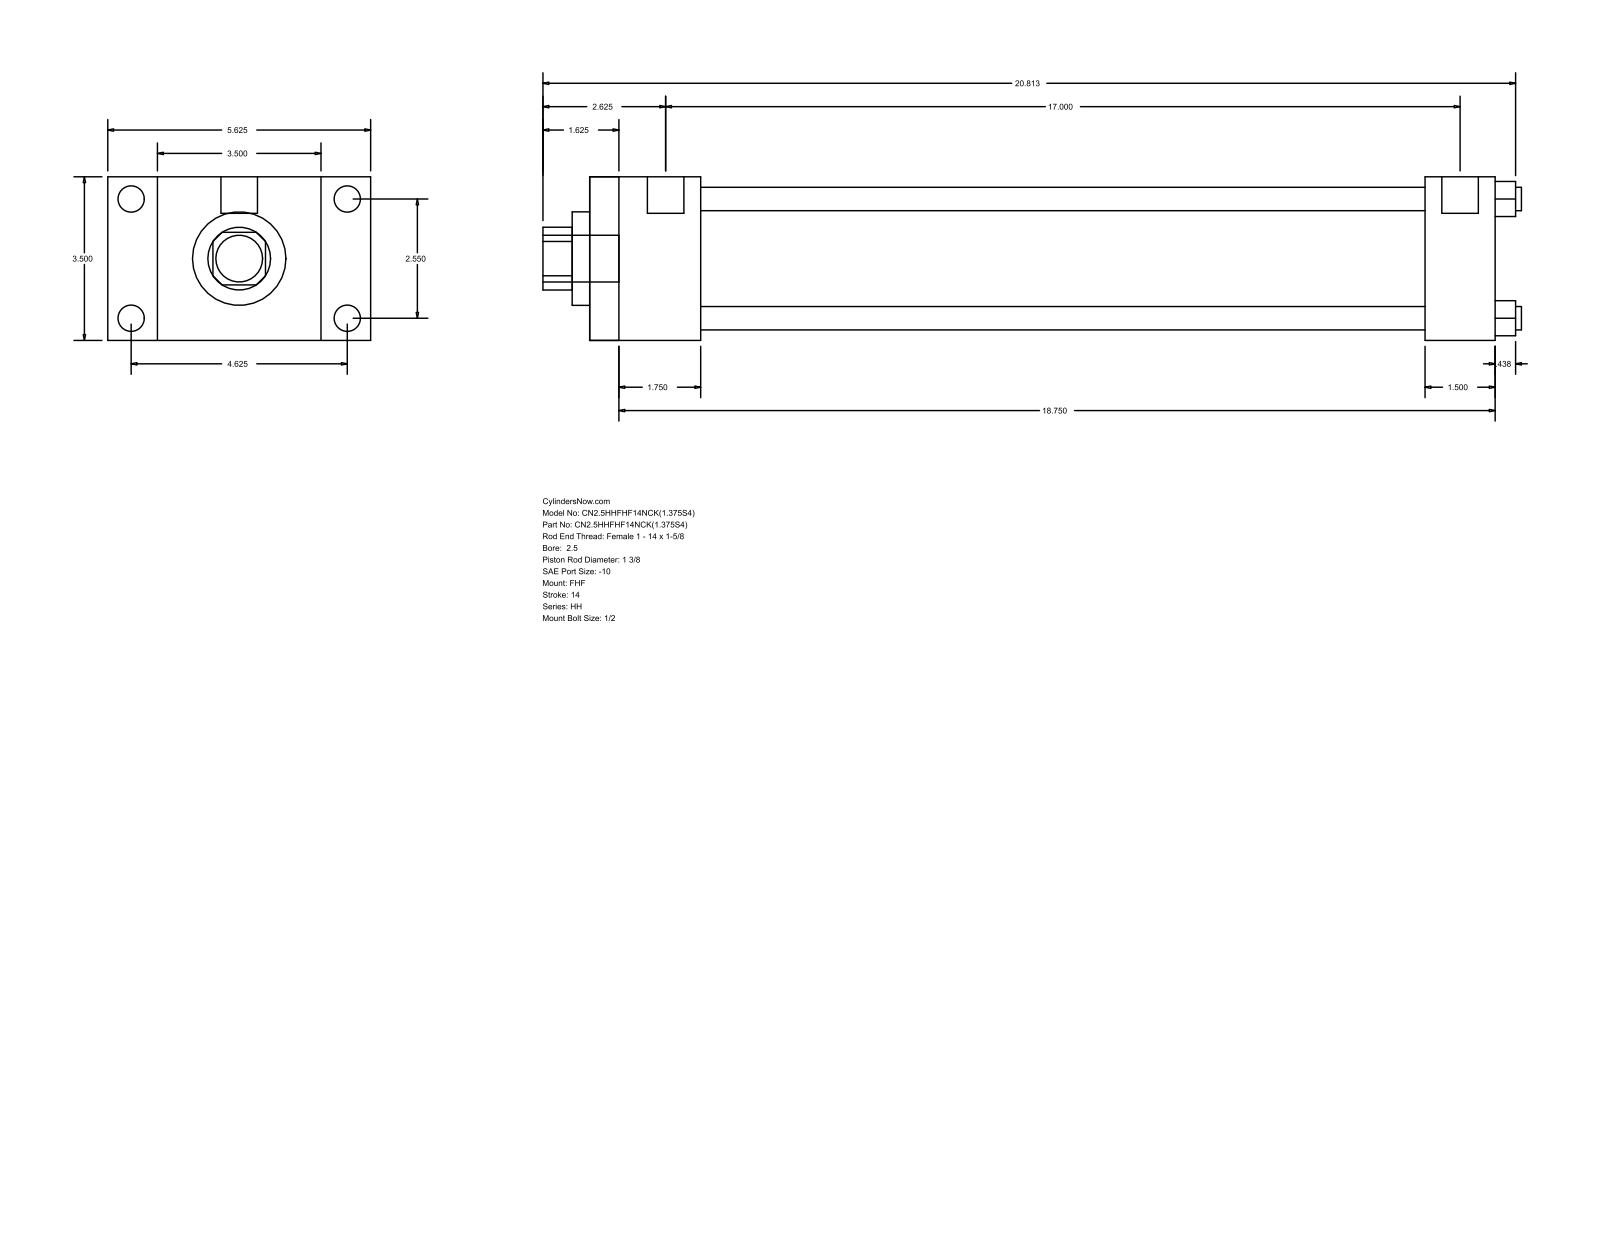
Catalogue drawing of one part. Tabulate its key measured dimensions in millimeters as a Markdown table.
| quantity | value |
| --- | --- |
| part name | HH_FHF__0250_1.375 |
| STEP written by | GSSL Pune (CONFIG_CONTROL_DESIGN) |
| units | millimeters |
| bodies | 0 solids, 88 faces (60 planar, 28 cylindrical, 0 other) |
| overall size | 531.81 × 142.88 × 88.9 |
| round holes (diameter × count) | 12.7 × 4, 34.92 × 1, 50.8 × 1, 73.03 × 1 |
| round bosses / shafts (diameter × count) | 14.3 × 4, 5.56 × 4, 19.84 × 2, 25.4 × 1 |
| partial cylindrical surfaces (radius × count) | 17.06 × 1 |
| main face-to-face distances | 88.9, 60.32, 26.99, 115.89, 492.12, 431.8, 142.88, 454.03, 393.71, 38.09 |
| hole center spacings | 45.79, 64.76, 91.58 |
